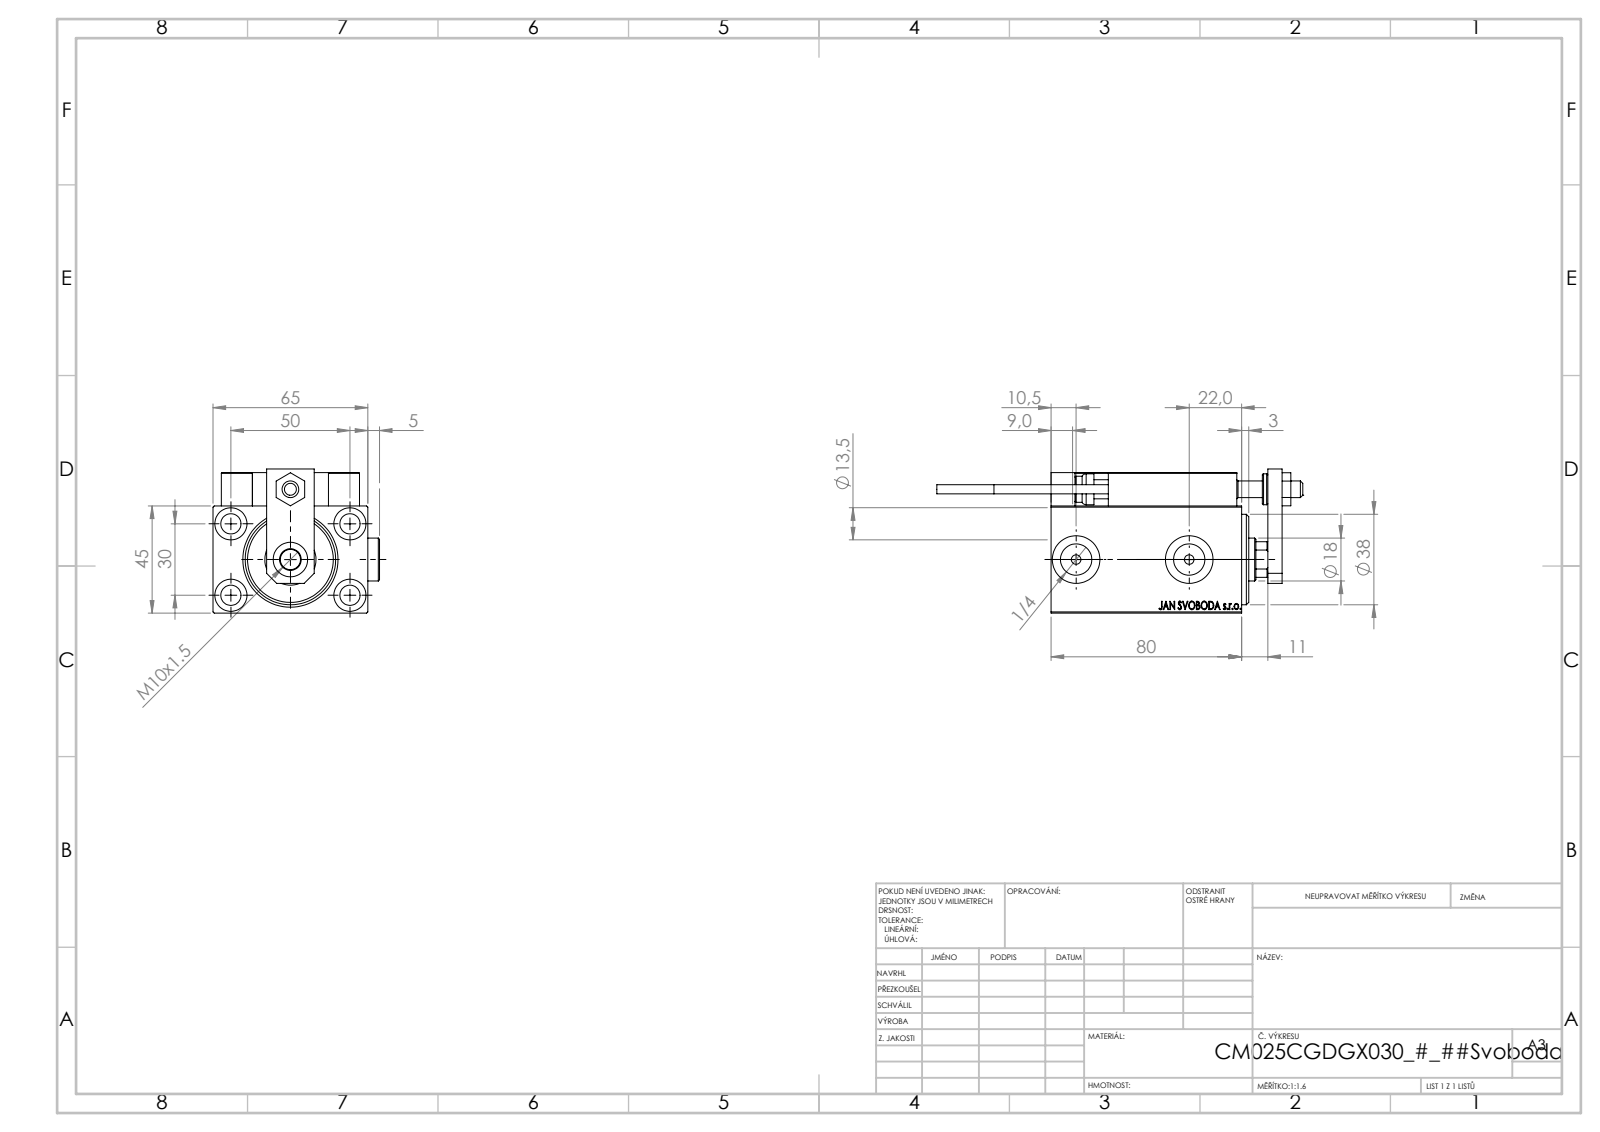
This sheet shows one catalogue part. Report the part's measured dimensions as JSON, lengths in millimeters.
{"part_name": "ALLEN BOLT D8; KONCOVKA; ZARAZKA; V450CM_C_VCP (+8 more)", "step_written_by": "SolidWorks 2019 (CONFIG_CONTROL_DESIGN)", "units": "millimeters", "bodies": {"solids": 25, "faces": 1336, "planar": 594, "cylindrical": 204, "other": 538}, "overall_size": [153.7, 69.9, 60.5], "volume_mm3": 246749, "surface_area_mm2": 76934, "round_holes": [[4, 6], [8, 5], [8.5, 5], [3.2, 4], [13.5, 4], [5, 2], [13.16, 2], [20, 2], [7, 1], [14.5, 1], [18, 1], [21.5, 1]], "round_bosses_or_shafts": [[18, 2], [5, 2], [3.8, 2], [13, 1], [11, 1]], "partial_cylinders_radius": [[0.3, 30], [3, 2], [8.5, 1]], "face_to_face_distances": [45, 65, 14, 59, 6, 3, 5, 13, 3.5, 7], "hole_center_spacings": [29.15, 11.37, 20, 28.9, 29.59, 29.69, 30, 32.06]}
